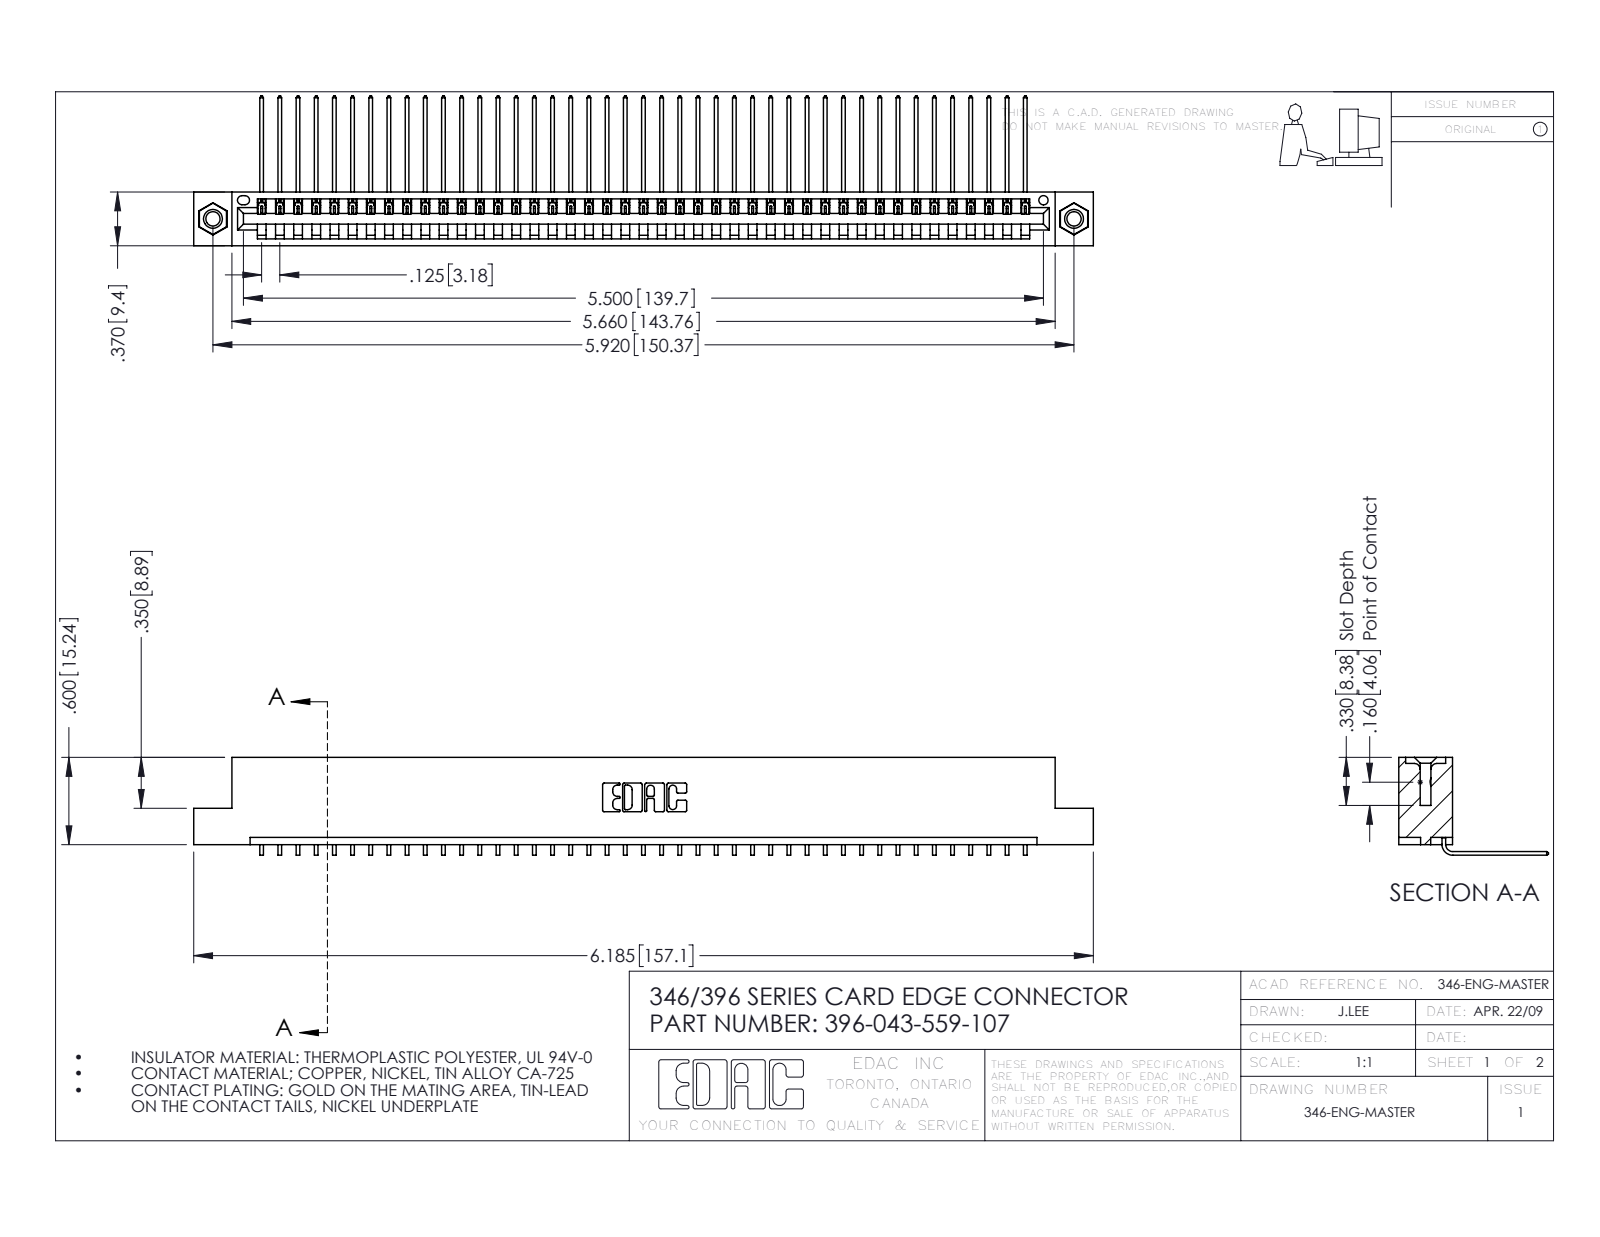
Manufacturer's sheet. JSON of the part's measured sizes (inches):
{"part_name": "345-292-001_558 559 Tail - 1; 345-250-001_345-250-005-103; 346 Part_Flush Mounting Lugs - 0.156 Dia-TI; 396-043-559-107", "step_written_by": "SolidWorks 2016 (CONFIG_CONTROL_DESIGN)", "units": "inches", "bodies": {"solids": 46, "faces": 2762, "planar": 1914, "cylindrical": 832, "other": 16}, "overall_size": [6.185, 1.03, 0.673], "volume_in3": 0.926, "surface_area_in2": 30.79, "round_holes": [[0.098, 2], [0.125, 2], [0.156, 2], [0.064, 1]], "round_bosses_or_shafts": [[0.155, 2]], "partial_cylinders_radius": [[0.006, 86], [0.01, 22], [0.007, 6], [0.031, 6], [0.026, 3], [0.031, 2], [0.04, 2], [0.014, 1]], "face_to_face_distances": [0.048, 0.322, 0.37, 0.025, 0.25, 0.072, 0.298, 0.148, 0.222, 0.1], "hole_center_spacings": [0.246, 5.711, 5.92]}
